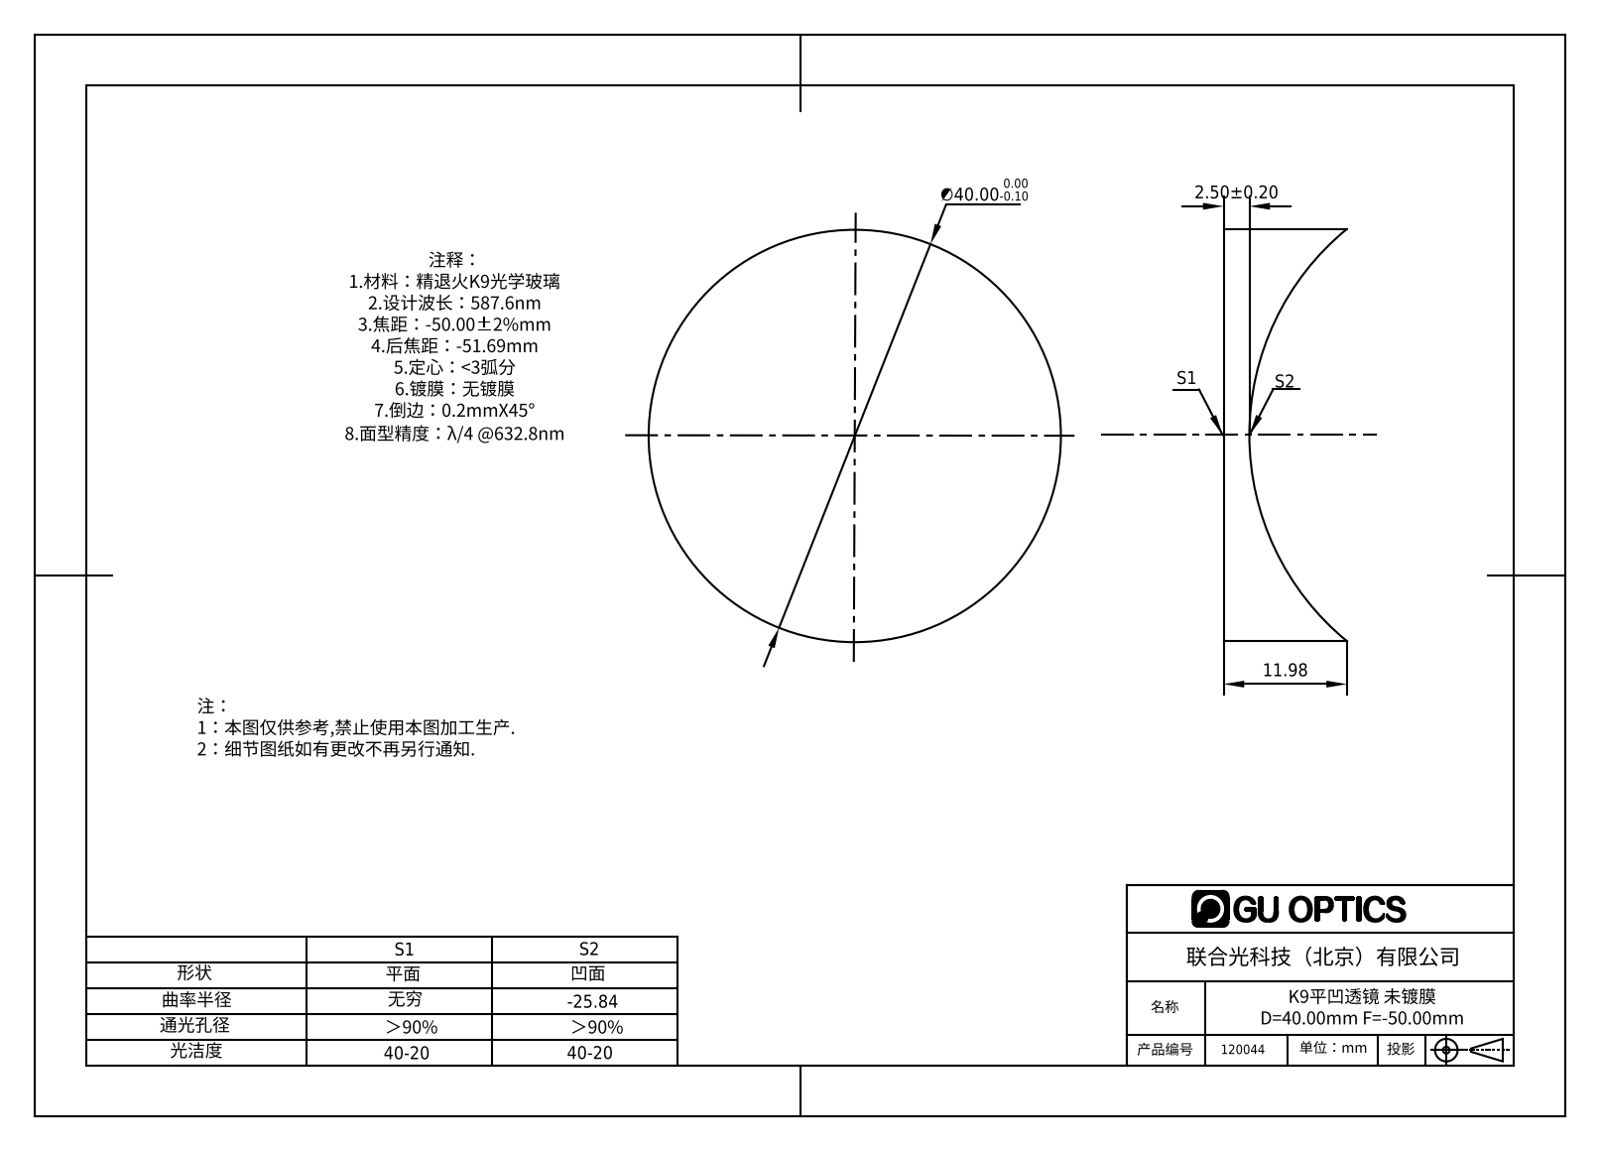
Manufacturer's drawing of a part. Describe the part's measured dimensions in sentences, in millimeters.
The part is named "120044". Its 3-D file was written by "SolidWorks 2016 (AUTOMOTIVE_DESIGN)". It is 1 solid with 5 faces: 1 planar, 2 cylindrical and 2 other. Overall it measures 40 by 40 by 11.98 millimeters. Its volume is 8 651 cubic millimeters and its surface area 4 301 square millimeters. Round bosses or shafts: 1 of diameter 40.
